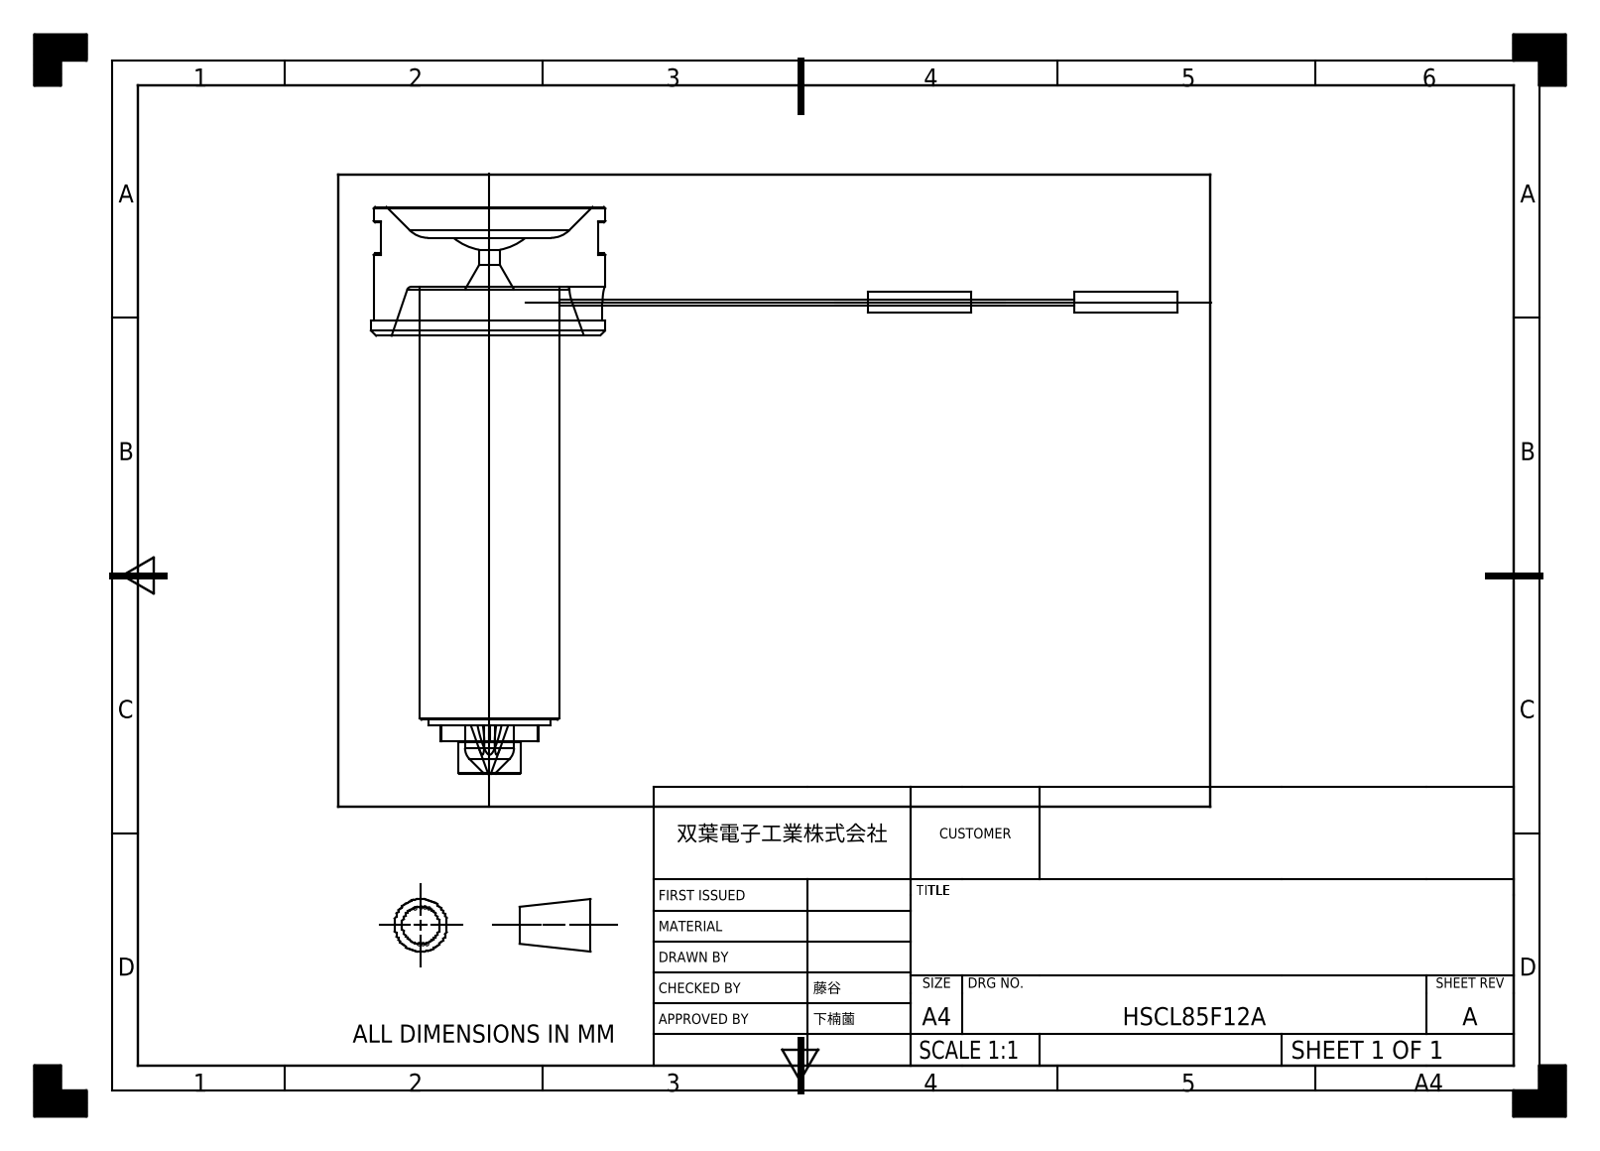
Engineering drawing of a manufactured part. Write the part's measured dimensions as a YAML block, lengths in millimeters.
part_name: "HSCL85F12A"
step_written_by: "SIEMENS PLM Software NX 2023 (AUTOMOTIVE_DESIGN)"
units: millimeters
bodies: {solids: 5, faces: 75, planar: 34, cylindrical: 23, other: 18}
overall_size: [156.5, 110, 46]
volume: 74829
surface_area: 17150
round_holes:
  - {diameter: 2.5, count: 1}
  - {diameter: 4, count: 1}
  - {diameter: 9.5, count: 1}
round_bosses_or_shafts:
  - {diameter: 4, count: 2}
  - {diameter: 1.2, count: 2}
  - {diameter: 46, count: 1}
  - {diameter: 45, count: 1}
  - {diameter: 27, count: 1}
  - {diameter: 23.8, count: 1}
  - {diameter: 12, count: 1}
partial_cylinders:
  - {radius: 2.8, count: 3}
  - {radius: 3, count: 2}
  - {radius: 10.9, count: 1}
face_to_face_distances: [9.5, 19, 6, 94.5, 25, 85, 103.7, 97.7, 78.7, 15.5]
